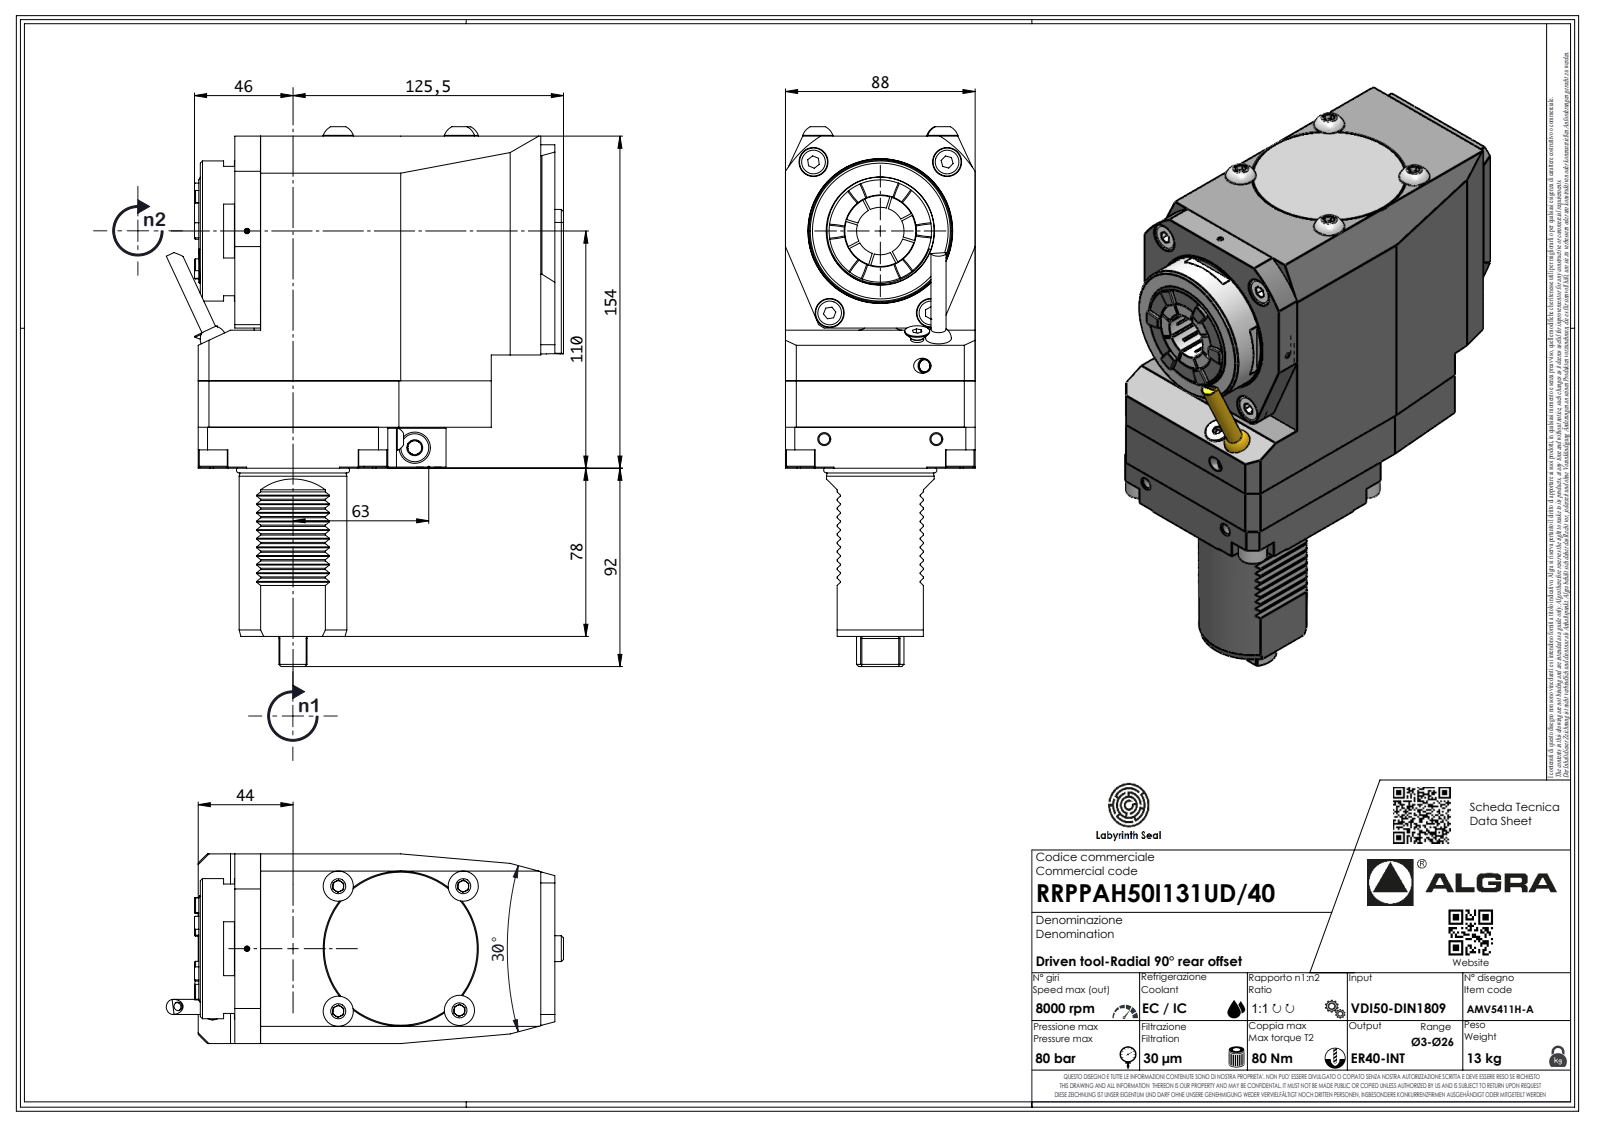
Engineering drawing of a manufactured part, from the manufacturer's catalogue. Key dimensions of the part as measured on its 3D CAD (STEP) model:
Part name (STEP PRODUCT): RRPPAH50I121UD40
STEP written by: SolidWorks 2023 (AUTOMOTIVE_DESIGN)
Units: millimetres
Bodies: 1 solid, 611 faces (430 planar, 87 cylindrical, 94 other)
Overall size (bounding box): 250.4 × 165.5 × 88
Volume: 2 010 000 mm³ · Surface area: 116 997 mm²
Round holes (diameter × count): ⌀2.1 ×1, ⌀10 ×1
Round bosses / shafts (diameter × count): ⌀14 ×4, ⌀13 ×4, ⌀65 ×1, ⌀50 ×1, ⌀48.7 ×1, ⌀6.37 ×1, ⌀1.7 ×1
Partial cylindrical surfaces — rounded edges, fillets, slot ends (radius × count): R0.3 ×22, R0.33 ×7, R0.52 ×7, R3.7 ×7, R6.75 ×4, R2 ×2, R4 ×2, R0.21 ×1
Main face-to-face distances: 88, 135, 154, 165.5, 19, 1, 17, 148.5, 16, 164.5
